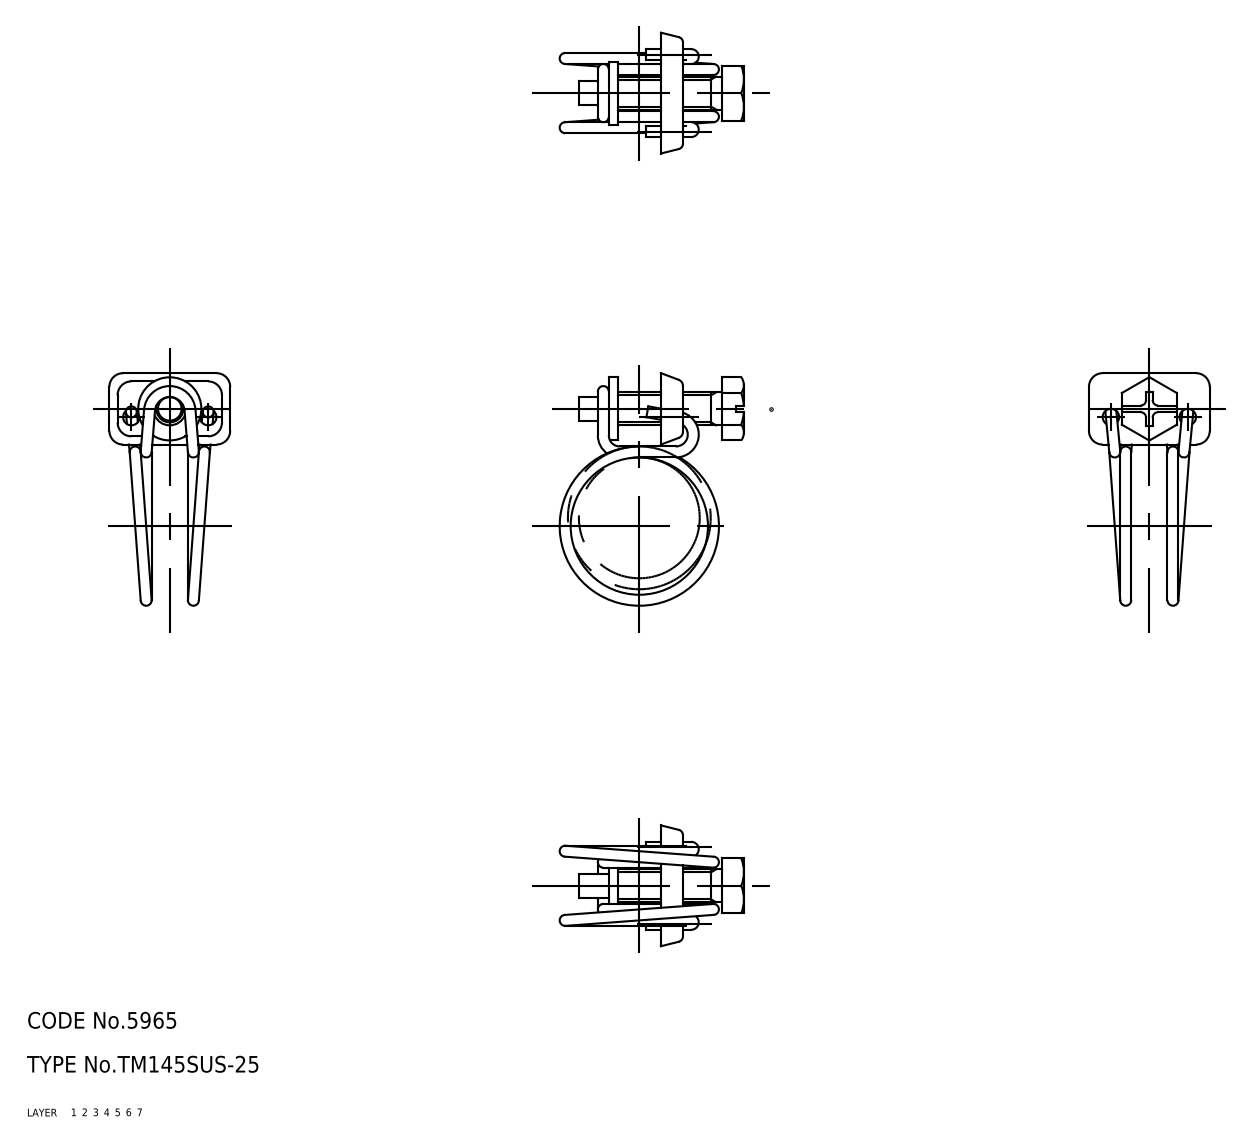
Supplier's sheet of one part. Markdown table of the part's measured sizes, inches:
| quantity | value |
| --- | --- |
| part name | screw; holder; band; TM_145SUS_25_21857_36 |
| STEP written by | CADfix (AUTOMOTIVE_DESIGN) |
| units | inches |
| bodies | 3 solids, 119 faces (0 planar, 0 cylindrical, 119 other) |
| overall size | 1.667 × 1.321 × 0.866 |
| volume | 0.145 in³ |
| surface area | 5.234 in² |
